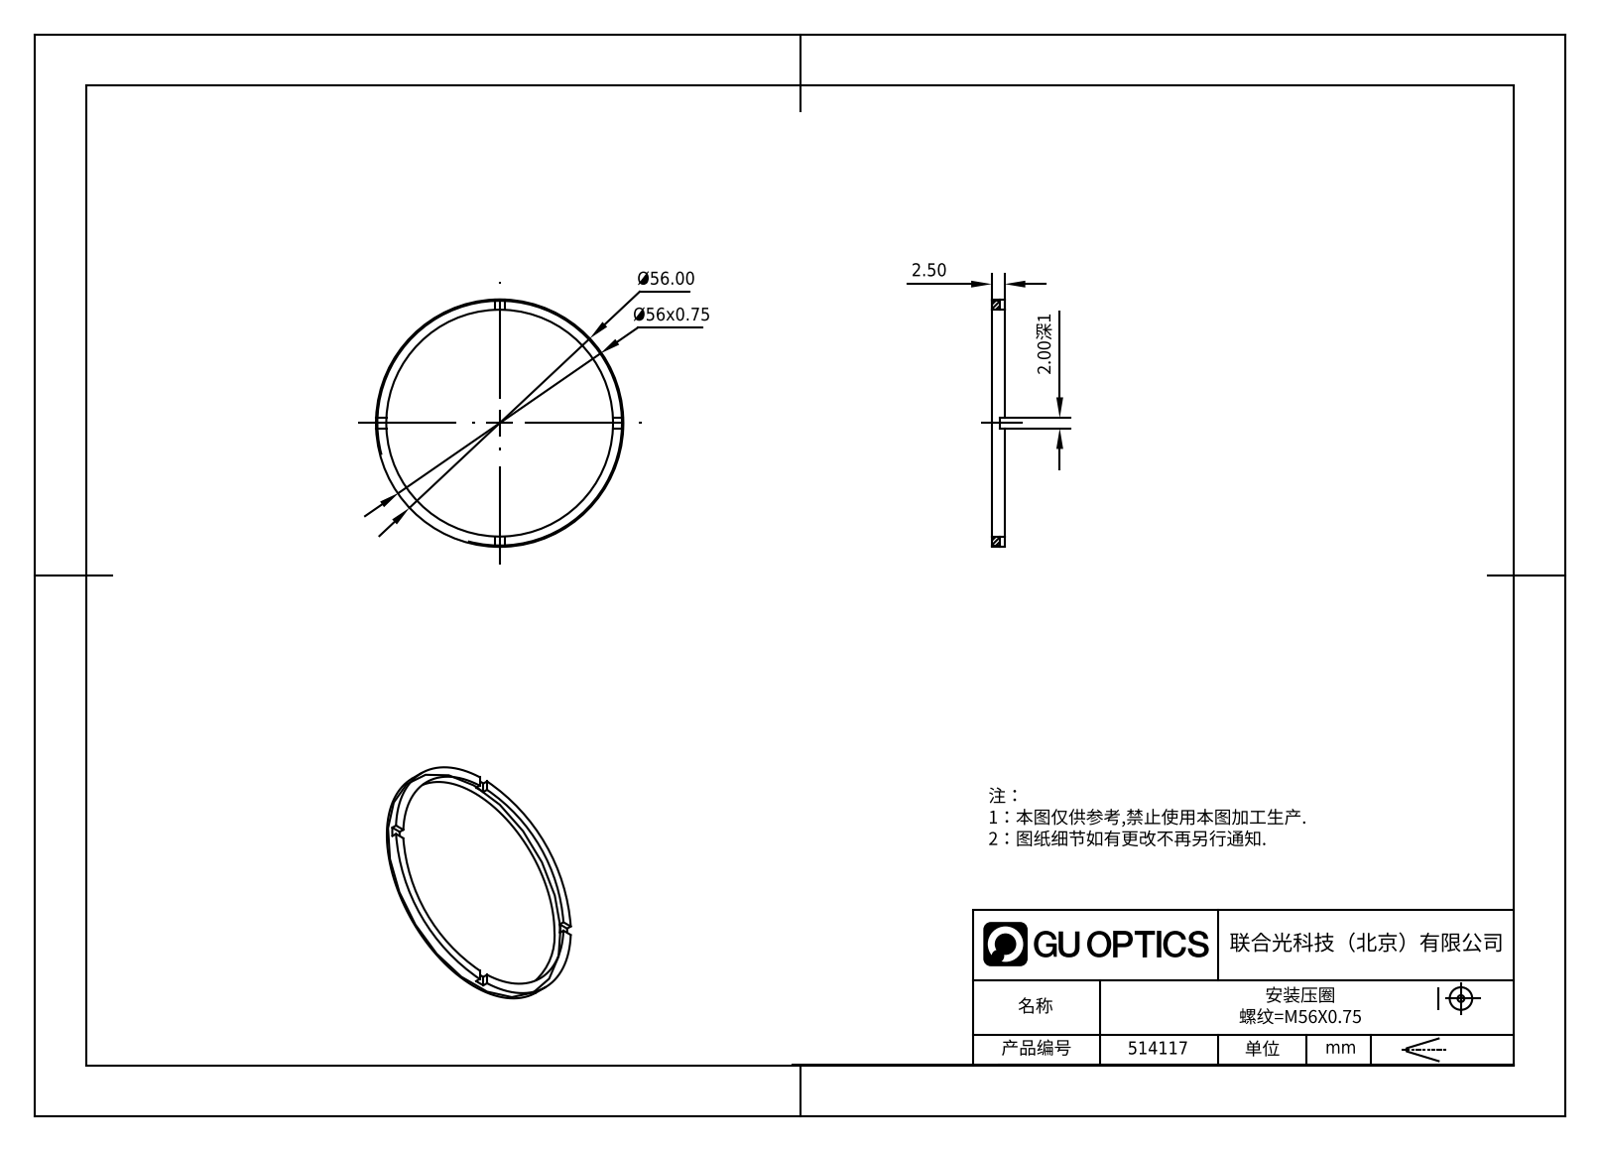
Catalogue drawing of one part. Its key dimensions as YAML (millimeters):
part_name: "514117"
step_written_by: "SolidWorks 2020 (CONFIG_CONTROL_DESIGN)"
units: millimeters
bodies: {solids: 1, faces: 21, planar: 17, cylindrical: 4, other: 0}
overall_size: [56, 56, 2.5]
volume: 1030
surface_area: 1685
round_holes:
  - {diameter: 51, count: 1}
round_bosses_or_shafts:
  - {diameter: 56, count: 1}
face_to_face_distances: [2.5, 1.5, 1, 2]
